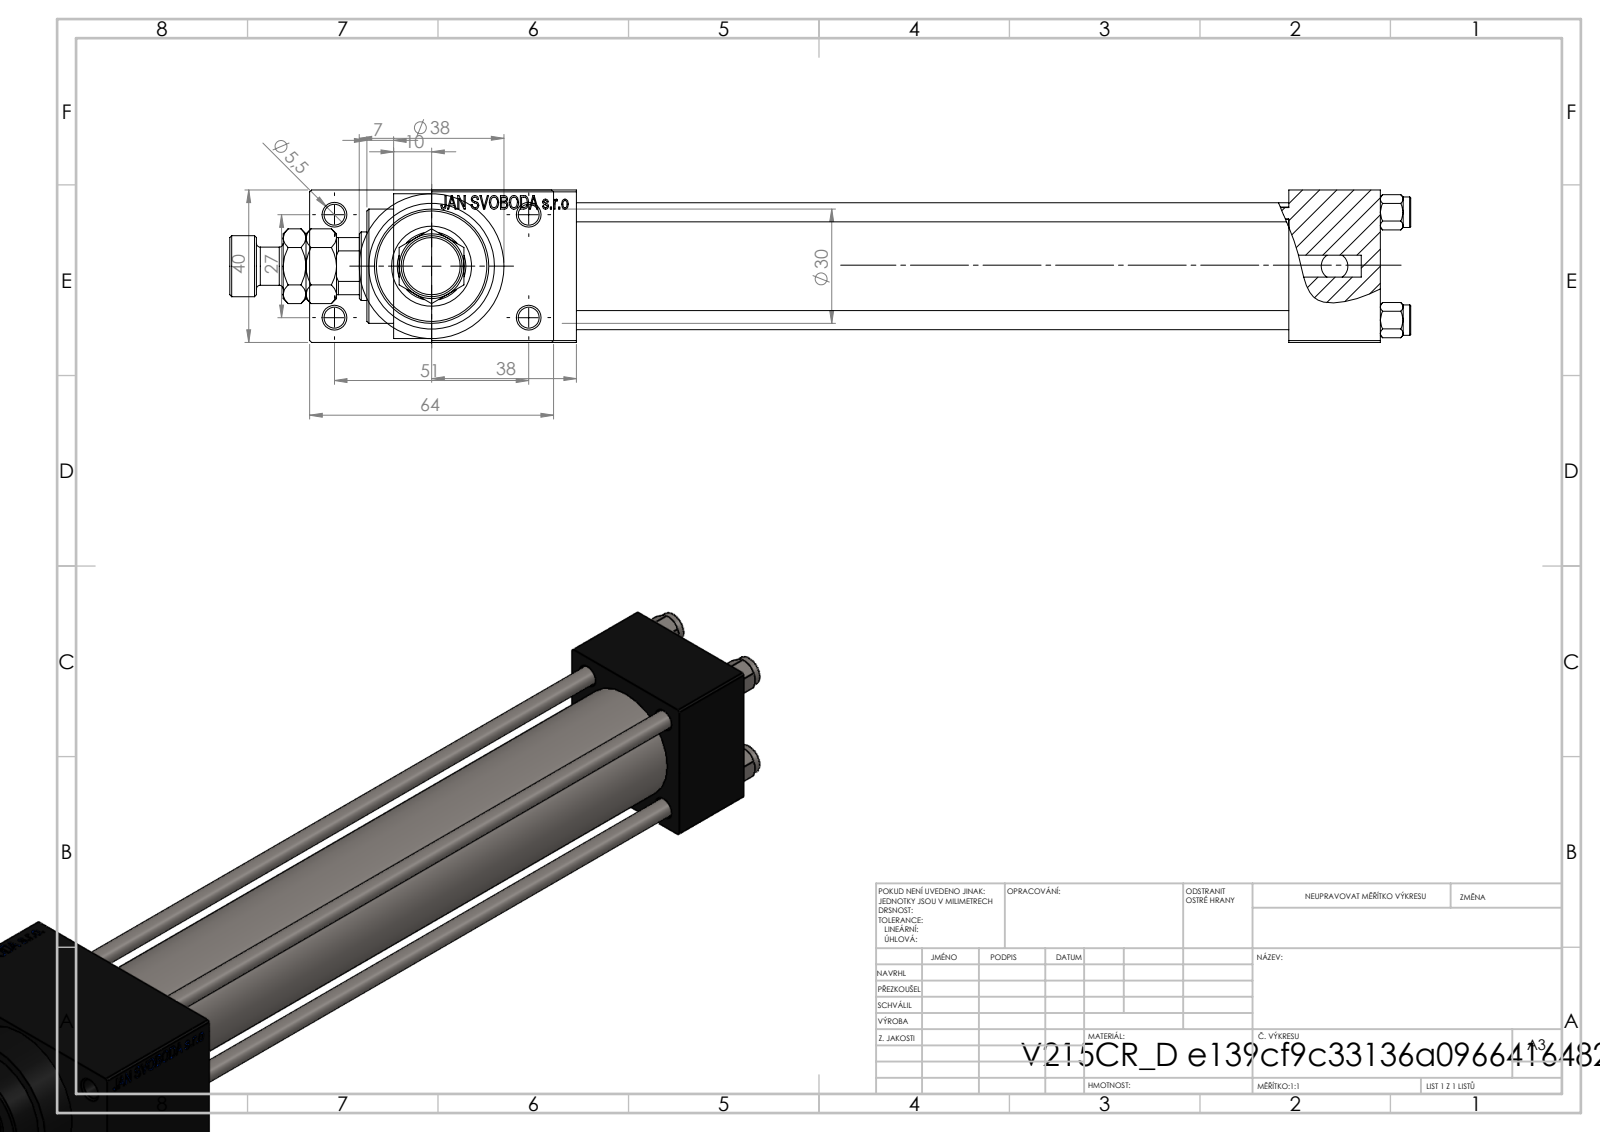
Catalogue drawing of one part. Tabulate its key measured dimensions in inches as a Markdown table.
| quantity | value |
| --- | --- |
| part name | MFA; V215_VC_A; NUT_M5_D; V215CR_D_Body (+2 more) |
| STEP written by | SolidWorks 2019 (CONFIG_CONTROL_DESIGN) |
| units | inches |
| bodies | 12 solids, 1153 faces (511 planar, 90 cylindrical, 552 other) |
| overall size | 12.205 × 2.52 × 1.575 |
| volume | 16.36 in³ |
| surface area | 167.5 in² |
| round holes (diameter × count) | 0.197 × 4, 0.217 × 4, 0.787 × 3, 0.276 × 2, 0.518 × 2, 0.335 × 1, 0.709 × 1, 0.827 × 1, 0.984 × 1, 1.181 × 1 |
| round bosses / shafts (diameter × count) | 0.315 × 4, 1.496 × 1, 1.22 × 1, 0.63 × 1, 0.394 × 1 |
| partial cylindrical surfaces (radius × count) | 0.335 × 1 |
| main face-to-face distances | 1.575, 0.472, 7.362, 0.945, 8.307, 2.047, 1.496, 9.803, 8.858, 2.52 |
| hole center spacings | 0.448, 0.788, 1.114, 1.136, 1.177, 1.561, 1.903, 1.063 |
